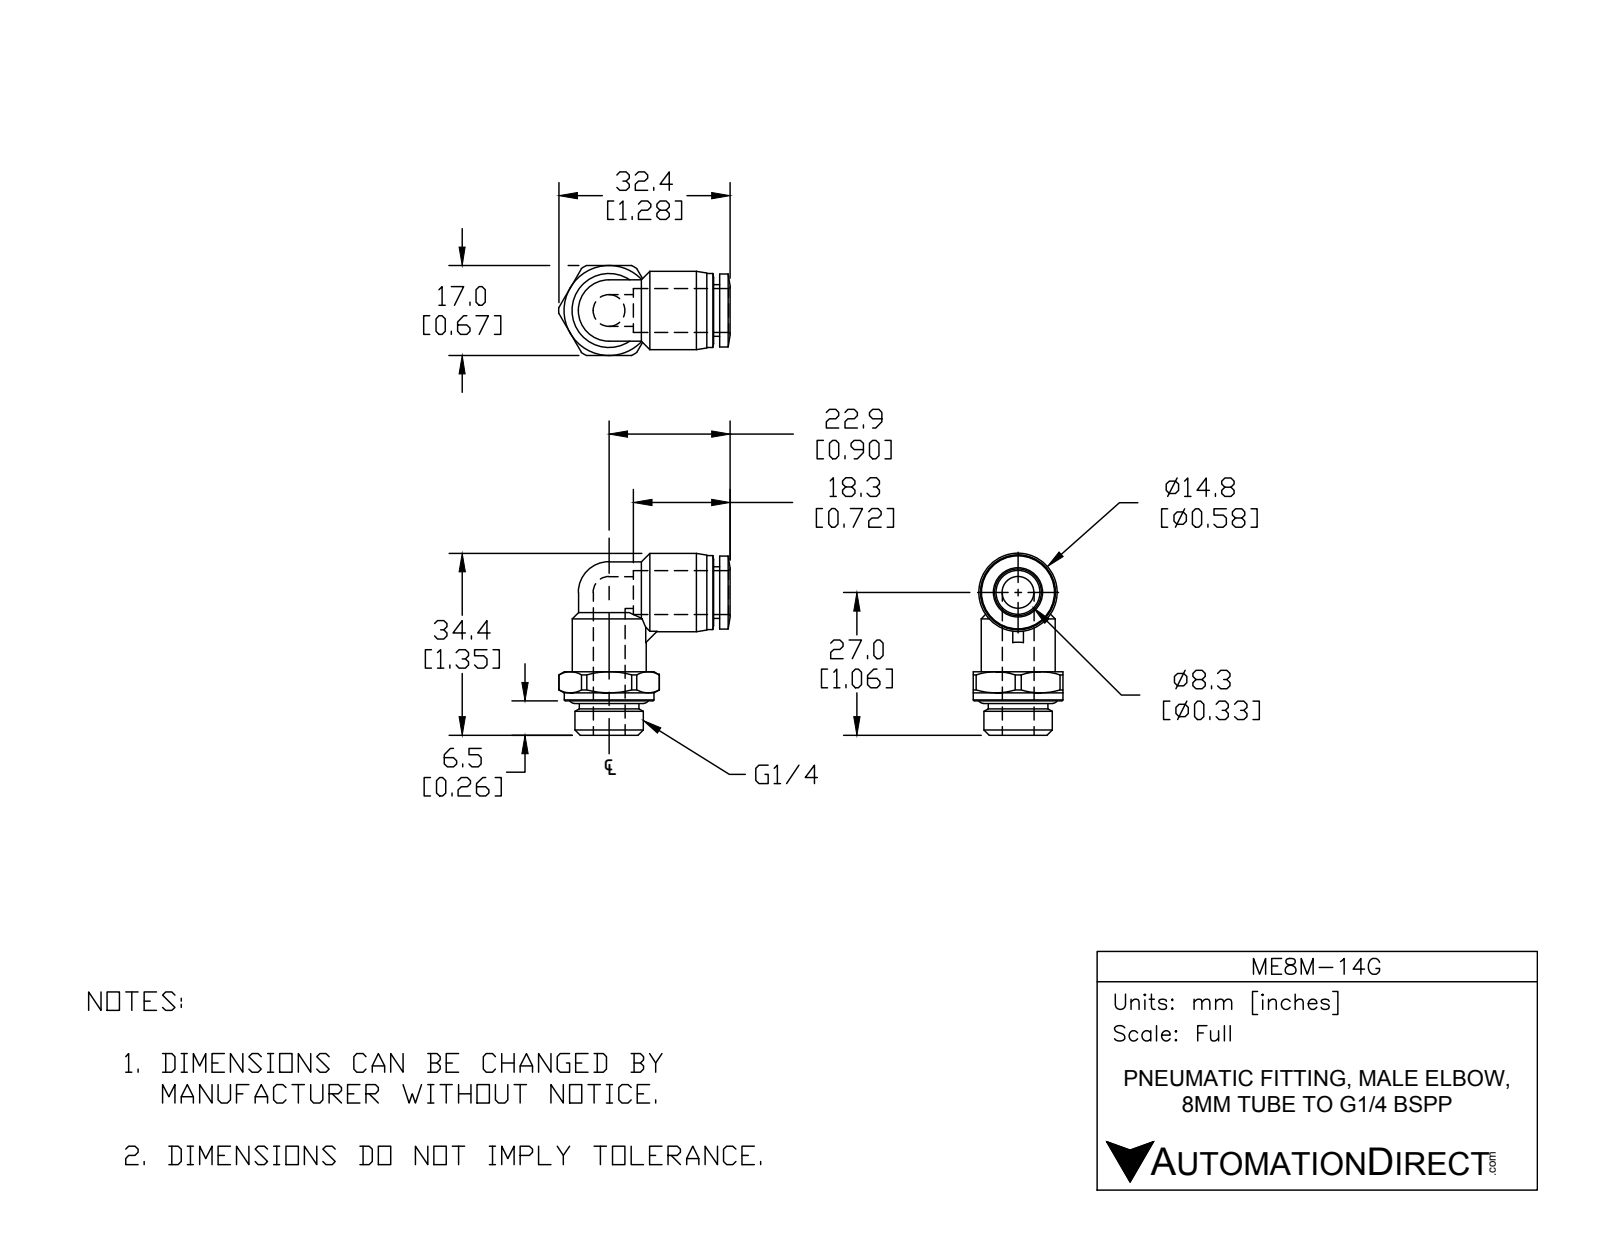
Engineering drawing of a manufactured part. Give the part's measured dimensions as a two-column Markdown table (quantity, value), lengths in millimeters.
| quantity | value |
| --- | --- |
| part name | ME8M-14G |
| STEP written by | SolidWorks 2018 (AUTOMOTIVE_DESIGN) |
| units | millimeters |
| bodies | 2 solids, 88 faces (18 planar, 31 cylindrical, 39 other) |
| overall size | 34.4 × 32.4 × 17 |
| volume | 5 560 mm³ |
| surface area | 4 108 mm² |
| round holes (diameter × count) | 6 × 2, 8.3 × 1 |
| round bosses / shafts (diameter × count) | 14 × 2, 17 × 1, 14.8 × 1, 13.8 × 1, 13 × 1, 11.6 × 1, 11.3 × 1, 9.8 × 1 |
| partial cylindrical surfaces (radius × count) | 5.8 × 1, 9.5 × 1 |
| main face-to-face distances | 17, 12, 1.1, 15.1, 16.3, 7.9, 4.1, 6.5, 1.4, 5.5 |
